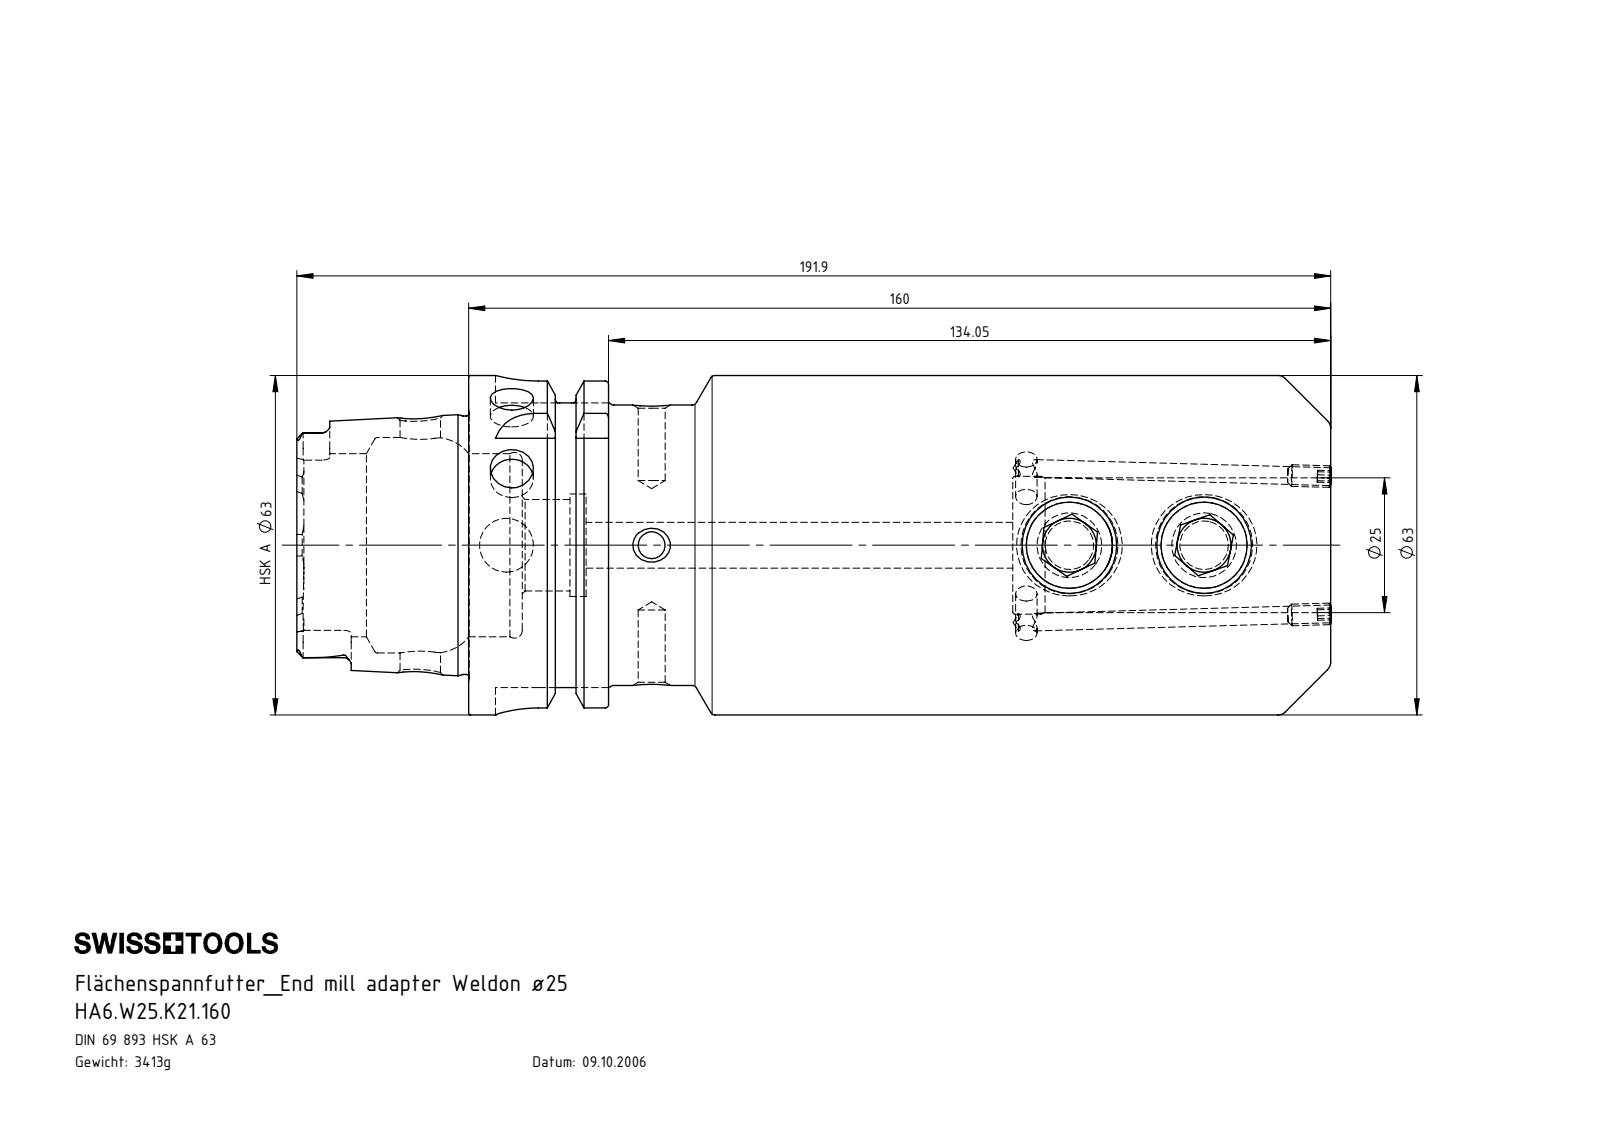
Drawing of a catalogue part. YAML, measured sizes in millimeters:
part_name: "HA6.W25.K21.160; ERU-CJ3.001.008; W25-ER1.001.020; HA6-W25.K21.160_C_Fertigbearbeitung"
step_written_by: "SolidWorks 2012 (CONFIG_CONTROL_DESIGN)"
units: millimeters
bodies: {solids: 5, faces: 331, planar: 97, cylindrical: 87, other: 147}
overall_size: [192, 63, 63]
volume: 434760
surface_area: 63026
round_holes:
  - {diameter: 3.3, count: 2}
  - {diameter: 5, count: 2}
  - {diameter: 8, count: 2}
  - {diameter: 16, count: 2}
  - {diameter: 4, count: 1}
  - {diameter: 7.5, count: 1}
  - {diameter: 8.5, count: 1}
  - {diameter: 10, count: 1}
  - {diameter: 17, count: 1}
  - {diameter: 19, count: 1}
  - {diameter: 25, count: 1}
  - {diameter: 25.6, count: 1}
round_bosses_or_shafts:
  - {diameter: 18, count: 2}
  - {diameter: 4, count: 2}
  - {diameter: 63, count: 1}
  - {diameter: 54.95, count: 1}
  - {diameter: 52, count: 1}
  - {diameter: 47.94, count: 1}
partial_cylinders:
  - {radius: 1.4, count: 6}
  - {radius: 2.88, count: 4}
  - {radius: 8, count: 4}
face_to_face_distances: [160, 25.95, 134.05, 16, 9.95, 150.05, 101, 91.05, 75.05, 59]
hole_center_spacings: [25, 26.95, 42.95, 77.55, 102.55, 104.5, 129.5]
